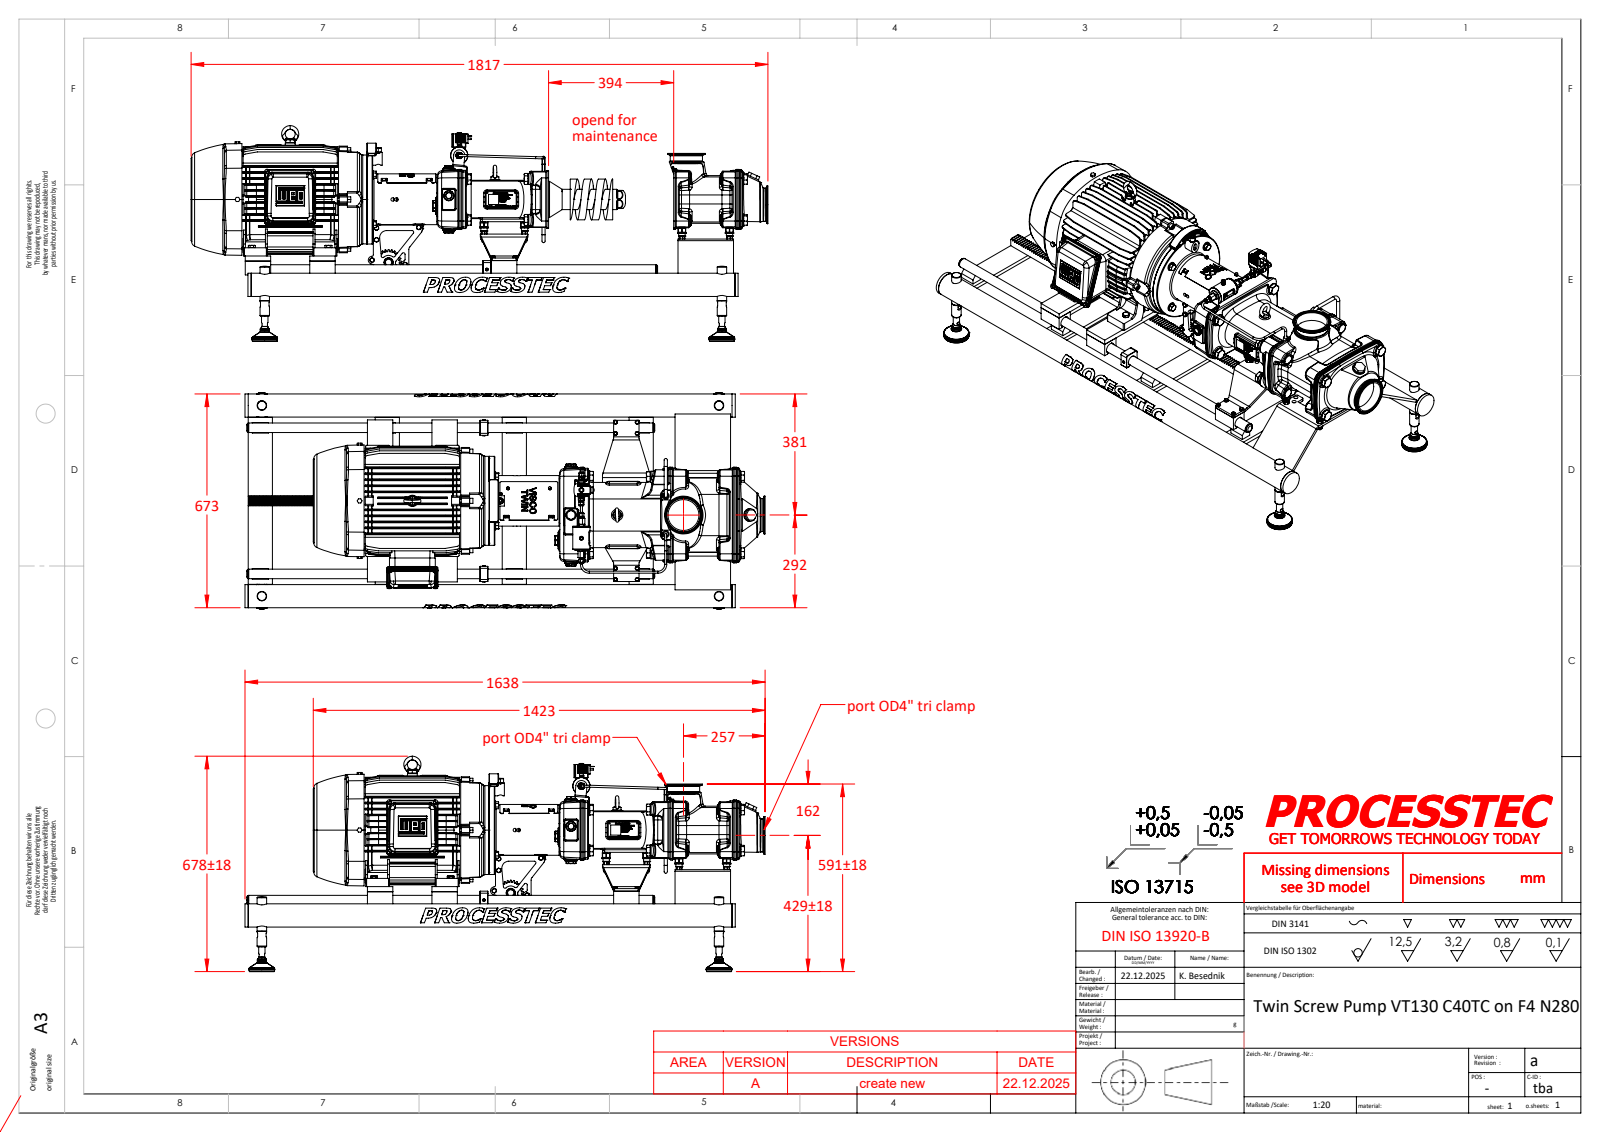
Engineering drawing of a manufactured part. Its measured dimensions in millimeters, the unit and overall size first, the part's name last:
Units: millimetres
Overall size (bounding box): 1638 × 680.5 × 678.26
Round holes (diameter × count): ⌀8.5 ×21, ⌀5 ×20, ⌀6.8 ×18, ⌀10.5 ×14, ⌀10.2 ×13, ⌀13 ×13, ⌀17.5 ×13, ⌀4.1 ×11, ⌀11 ×10, ⌀17 ×9, ⌀6.4 ×8, ⌀10.1 ×8
Round bosses / shafts (diameter × count): ⌀10 ×36, ⌀6 ×29, ⌀8 ×18, ⌀12 ×17, ⌀20 ×16, ⌀24 ×12, ⌀17 ×11, ⌀13 ×11
Partial cylindrical surfaces — rounded edges, fillets, slot ends (radius × count): R2 ×118, R4 ×87, R3 ×86, R1.5 ×73, R0.5 ×58, R0.48 ×50, R6 ×49, R8 ×48
Main face-to-face distances: 12.7, 8, 81, 68.3, 97.4, 84.7, 16.4, 481, 202, 554
Hole centre spacings: 461.41, 400, 129.3, 230, 832.41, 55, 609.59, 800
Volume: 82 940 000 mm³ · Surface area: 7 600 000 mm²
Bodies: 227 solids, 19384 faces (7557 planar, 3532 cylindrical, 8295 other)
Part name (STEP PRODUCT): 000957; 001328; 001016; 000992_mid (+8 more)
STEP written by: SolidWorks 2023 (AUTOMOTIVE_DESIGN)
